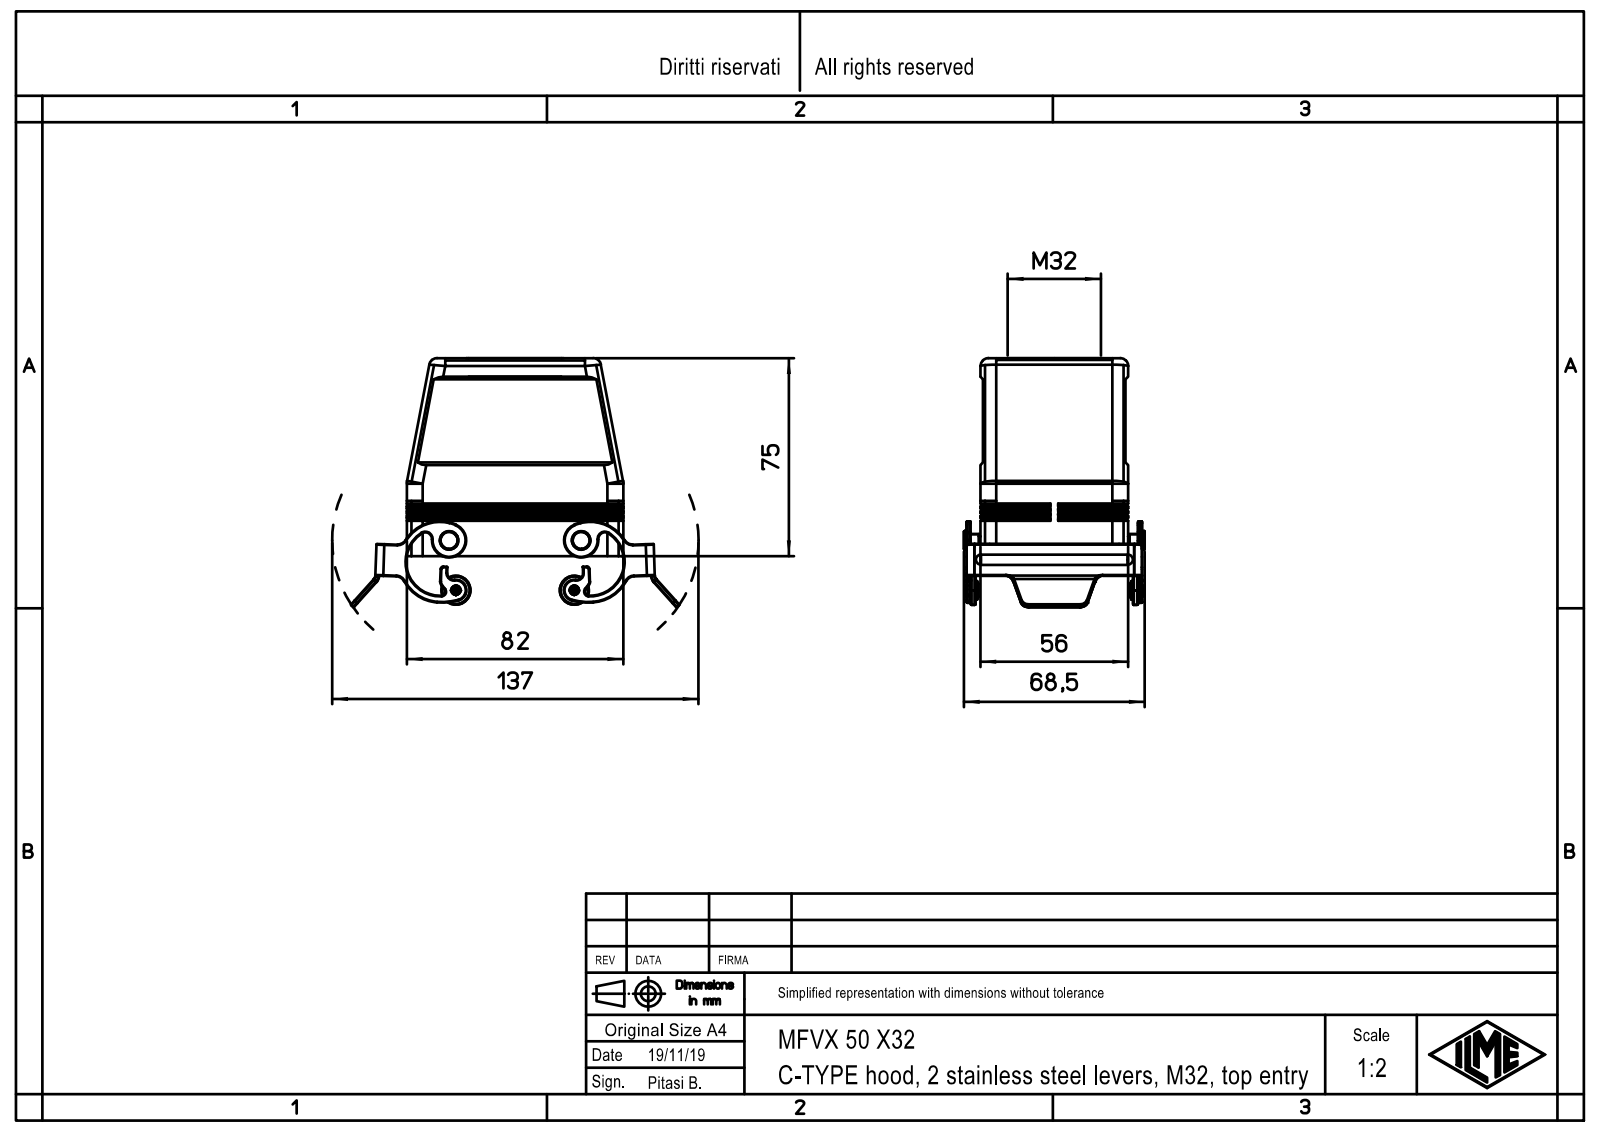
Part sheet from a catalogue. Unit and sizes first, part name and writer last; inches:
Units: inches
Overall size (bounding box): 4.834 × 3.766 × 2.697
Round holes (diameter × count): ⌀0.097 ×8, ⌀0.138 ×8, ⌀0.197 ×4, ⌀0.047 ×2, ⌀0.079 ×2, ⌀0.122 ×2, ⌀1.26 ×1
Round bosses / shafts (diameter × count): ⌀0.276 ×4, ⌀0.189 ×4, ⌀0.118 ×4, ⌀0.433 ×2, ⌀0.138 ×2, ⌀1.575 ×1
Partial cylindrical surfaces — rounded edges, fillets, slot ends (radius × count): R0.118 ×20, R0.079 ×12, R0.236 ×10, R0.059 ×6, R0.138 ×6, R0.217 ×6, R0.098 ×4, R0.157 ×4
Main face-to-face distances: 0.118, 2.087, 0.039, 1.969, 0.079, 2.165, 2.047, 0.325, 0.059, 2.205
Hole centre spacings: 0.63, 0.945, 1.309, 1.519, 2.598, 2.674, 2.765, 0.315
Volume: 5.198 in³ · Surface area: 88.6 in²
Bodies: 3 solids, 691 faces (277 planar, 320 cylindrical, 94 other)
Part name (STEP PRODUCT): MFVX 50 X32; Leva; Leva.1
STEP written by: Creo Elements/Direct Modeling 20.1B 02-Apr-2019 (C) Parametric Technology GmbH (AUTOMOTIVE_DESIGN)
